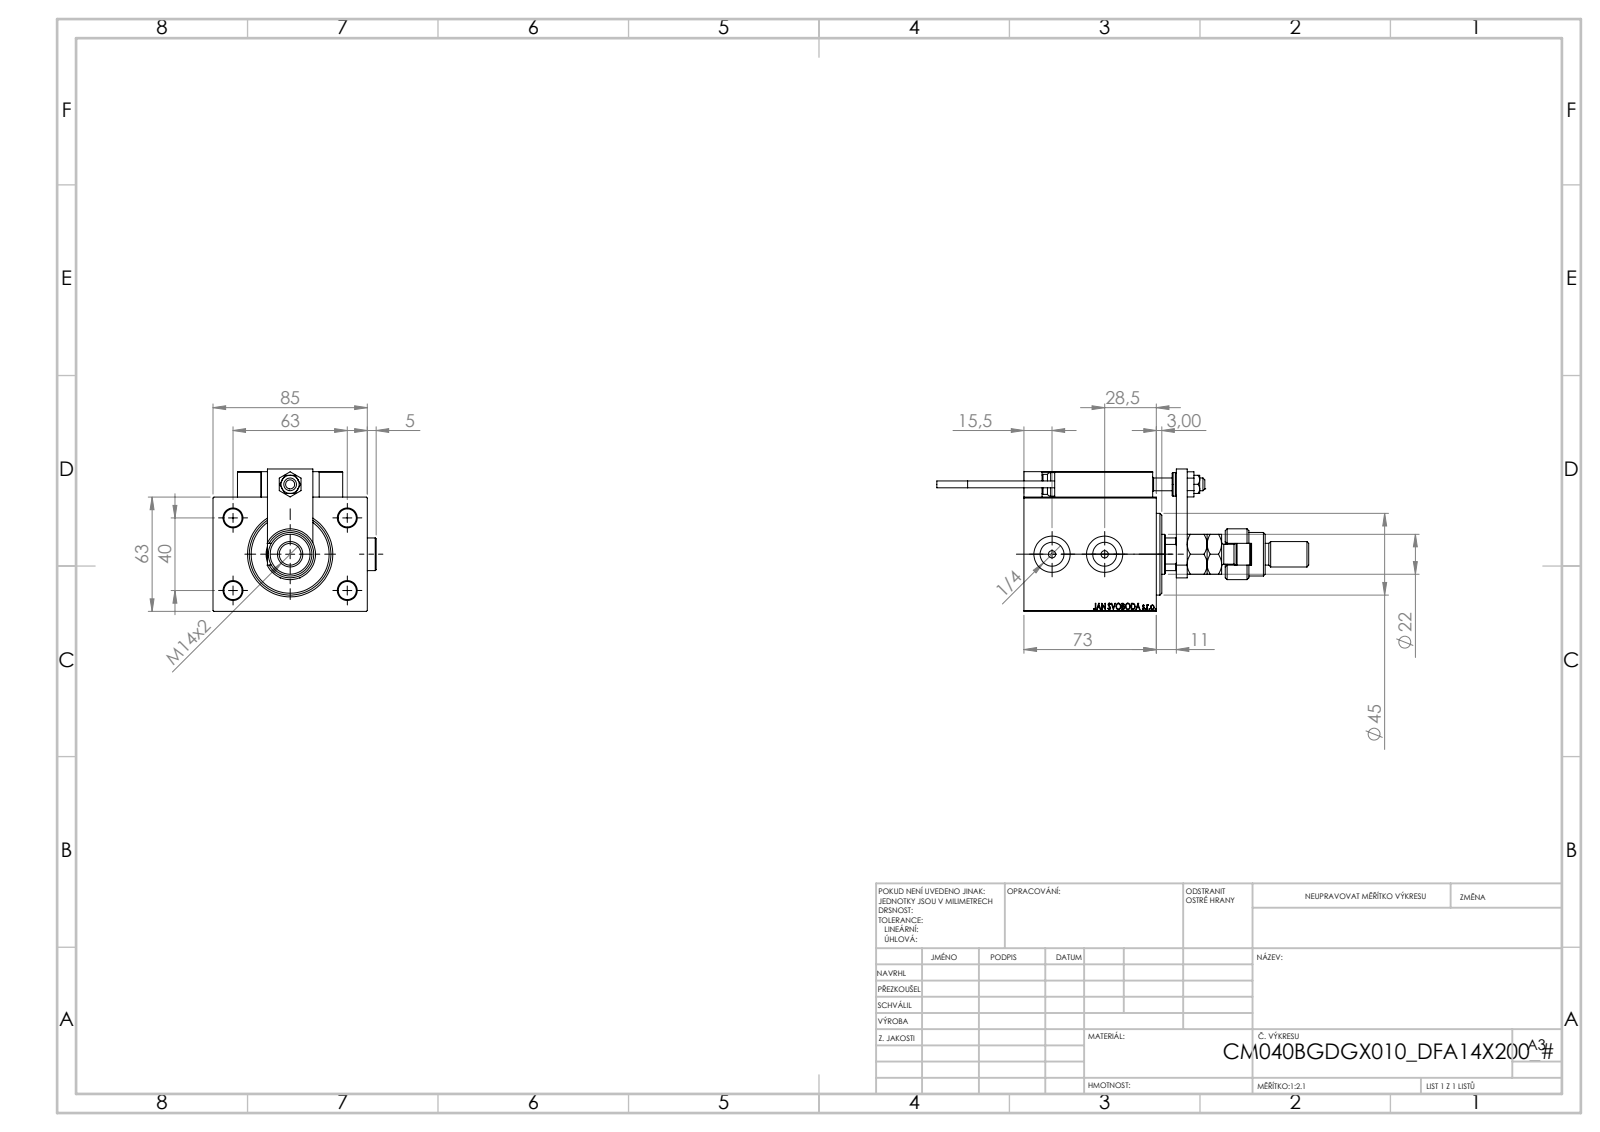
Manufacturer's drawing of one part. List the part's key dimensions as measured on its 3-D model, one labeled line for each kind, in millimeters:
Part name (STEP PRODUCT): NUT_D10; NUT_D12; KONCOVKA; ZARAZKA (+7 more)
STEP written by: SolidWorks 2019 (CONFIG_CONTROL_DESIGN)
Units: millimetres
Bodies: 28 solids, 1455 faces (623 planar, 211 cylindrical, 621 other)
Overall size (bounding box): 205 × 89.9 × 78.5
Volume: 437 523 mm³ · Surface area: 97 183 mm²
Round holes (diameter × count): ⌀4 ×6, ⌀8 ×5, ⌀3.2 ×4, ⌀10 ×4, ⌀5 ×2, ⌀13.16 ×2, ⌀20 ×2, ⌀7 ×1, ⌀12.5 ×1, ⌀16.5 ×1, ⌀22 ×1, ⌀25.5 ×1
Round bosses / shafts (diameter × count): ⌀18 ×3, ⌀11 ×2, ⌀5 ×2, ⌀3.8 ×2, ⌀28 ×1, ⌀24 ×1, ⌀14 ×1, ⌀13 ×1
Partial cylindrical surfaces — rounded edges, fillets, slot ends (radius × count): R0.3 ×30, R3 ×2, R9.75 ×1, R10.5 ×1
Main face-to-face distances: 63, 22, 85, 73, 14, 51, 17, 10, 77, 68
Hole centre spacings: 37.31, 11.37, 20, 25.08, 29.59, 29.69, 33.3, 35.57
